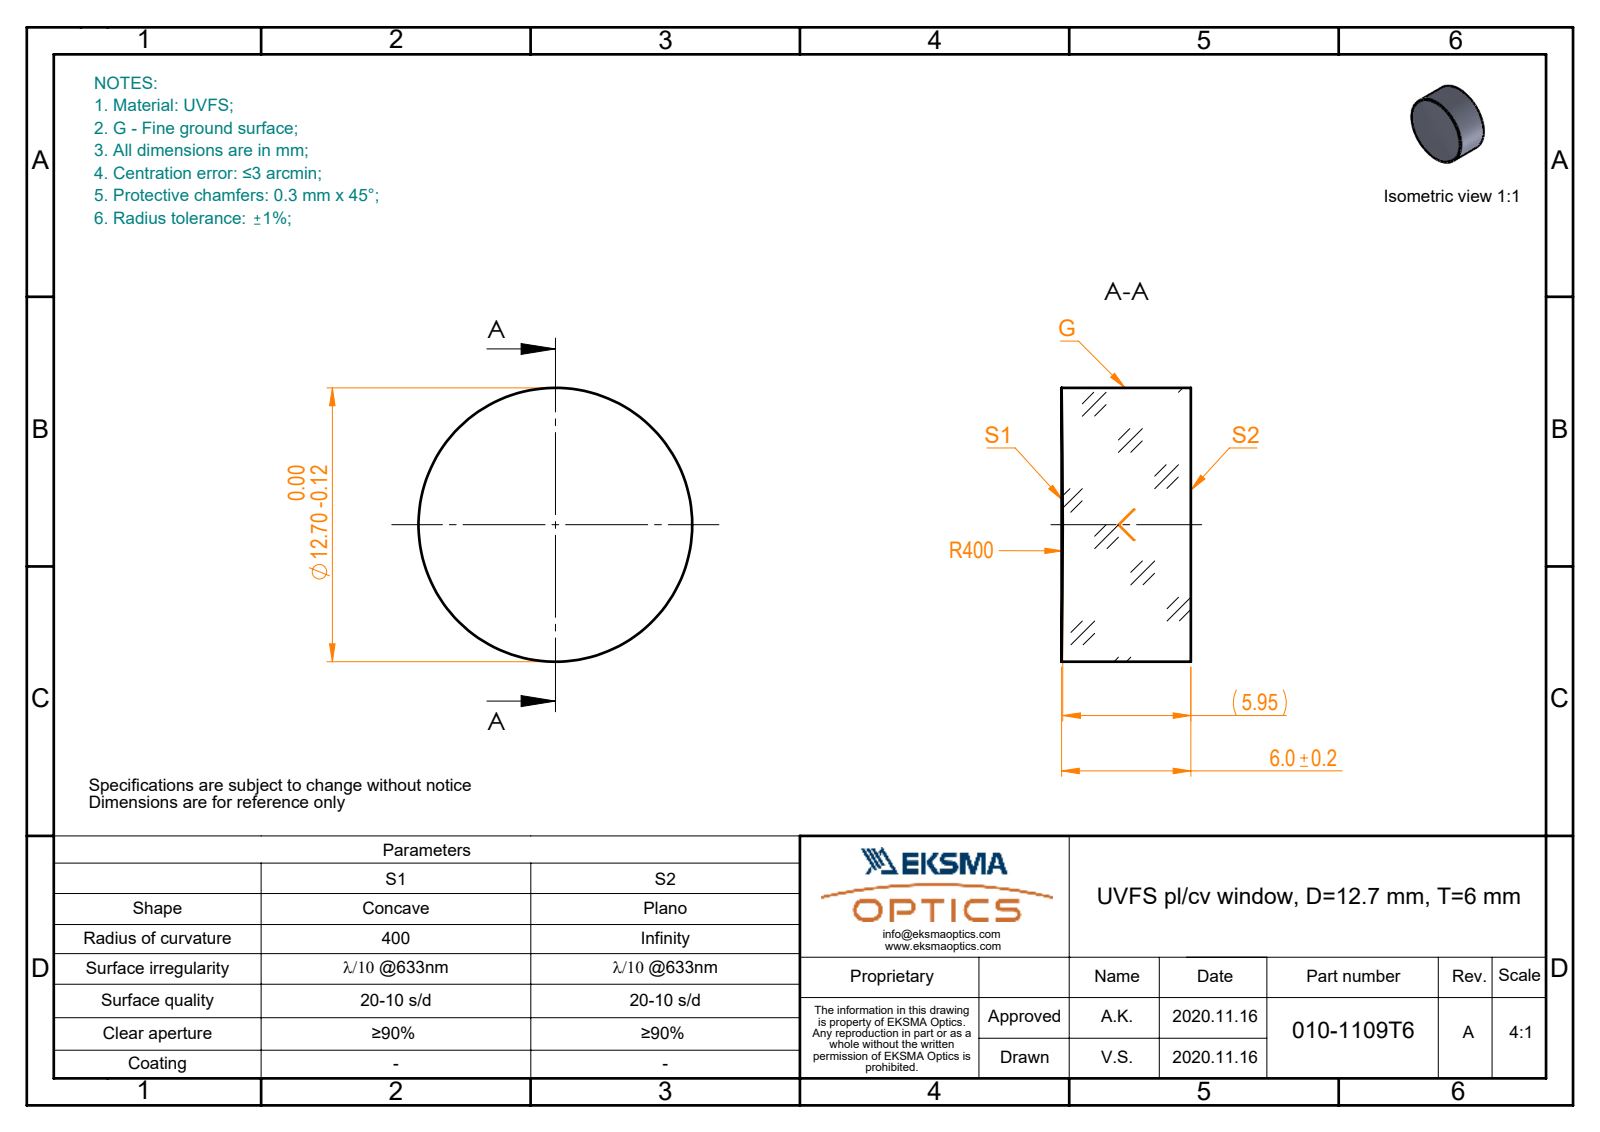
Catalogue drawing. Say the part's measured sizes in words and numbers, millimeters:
The part is named "010-1109T6_UVFS_PCV_window". Its 3-D file was written by "SolidWorks 2019 (CONFIG_CONTROL_DESIGN)". It is 1 solid with 5 faces: 1 planar, 2 cylindrical and 2 other. Overall it measures 12.7 by 12.7 by 6 millimeters. Its volume is 757 cubic millimeters and its surface area 493 square millimeters. Round bosses or shafts: 1 of diameter 12.7.
